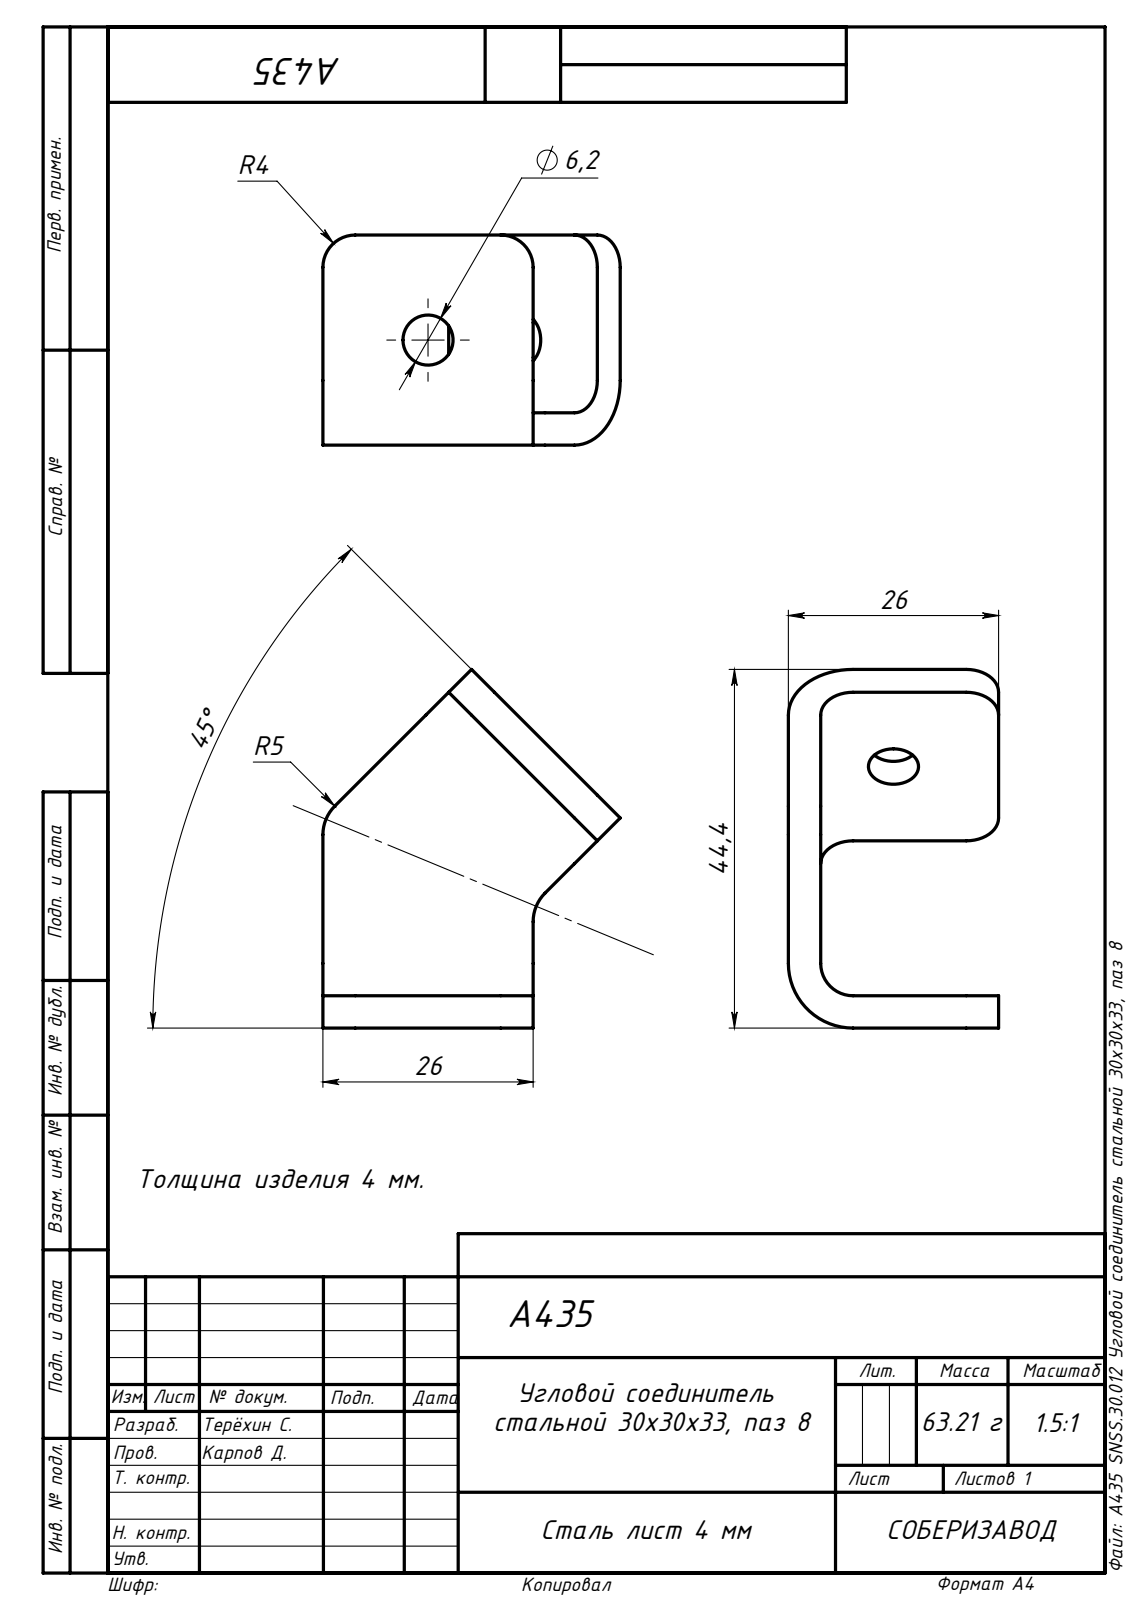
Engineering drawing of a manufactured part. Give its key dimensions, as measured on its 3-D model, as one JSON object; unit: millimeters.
{"part_name": "A435 SNSS.30.012 Угловой соединитель стальной 30х30х33, паз 8", "step_written_by": "SolidWorks 2020 (AUTOMOTIVE_DESIGN)", "units": "millimeters", "bodies": {"solids": 1, "faces": 34, "planar": 20, "cylindrical": 14, "other": 0}, "overall_size": [44.38, 36.77, 26], "volume_mm3": 8032, "surface_area_mm2": 4991, "round_holes": [[6.2, 2]], "partial_cylinders_radius": [[4, 6], [5, 2], [8, 2]], "face_to_face_distances": [4, 26, 22, 25.99]}
